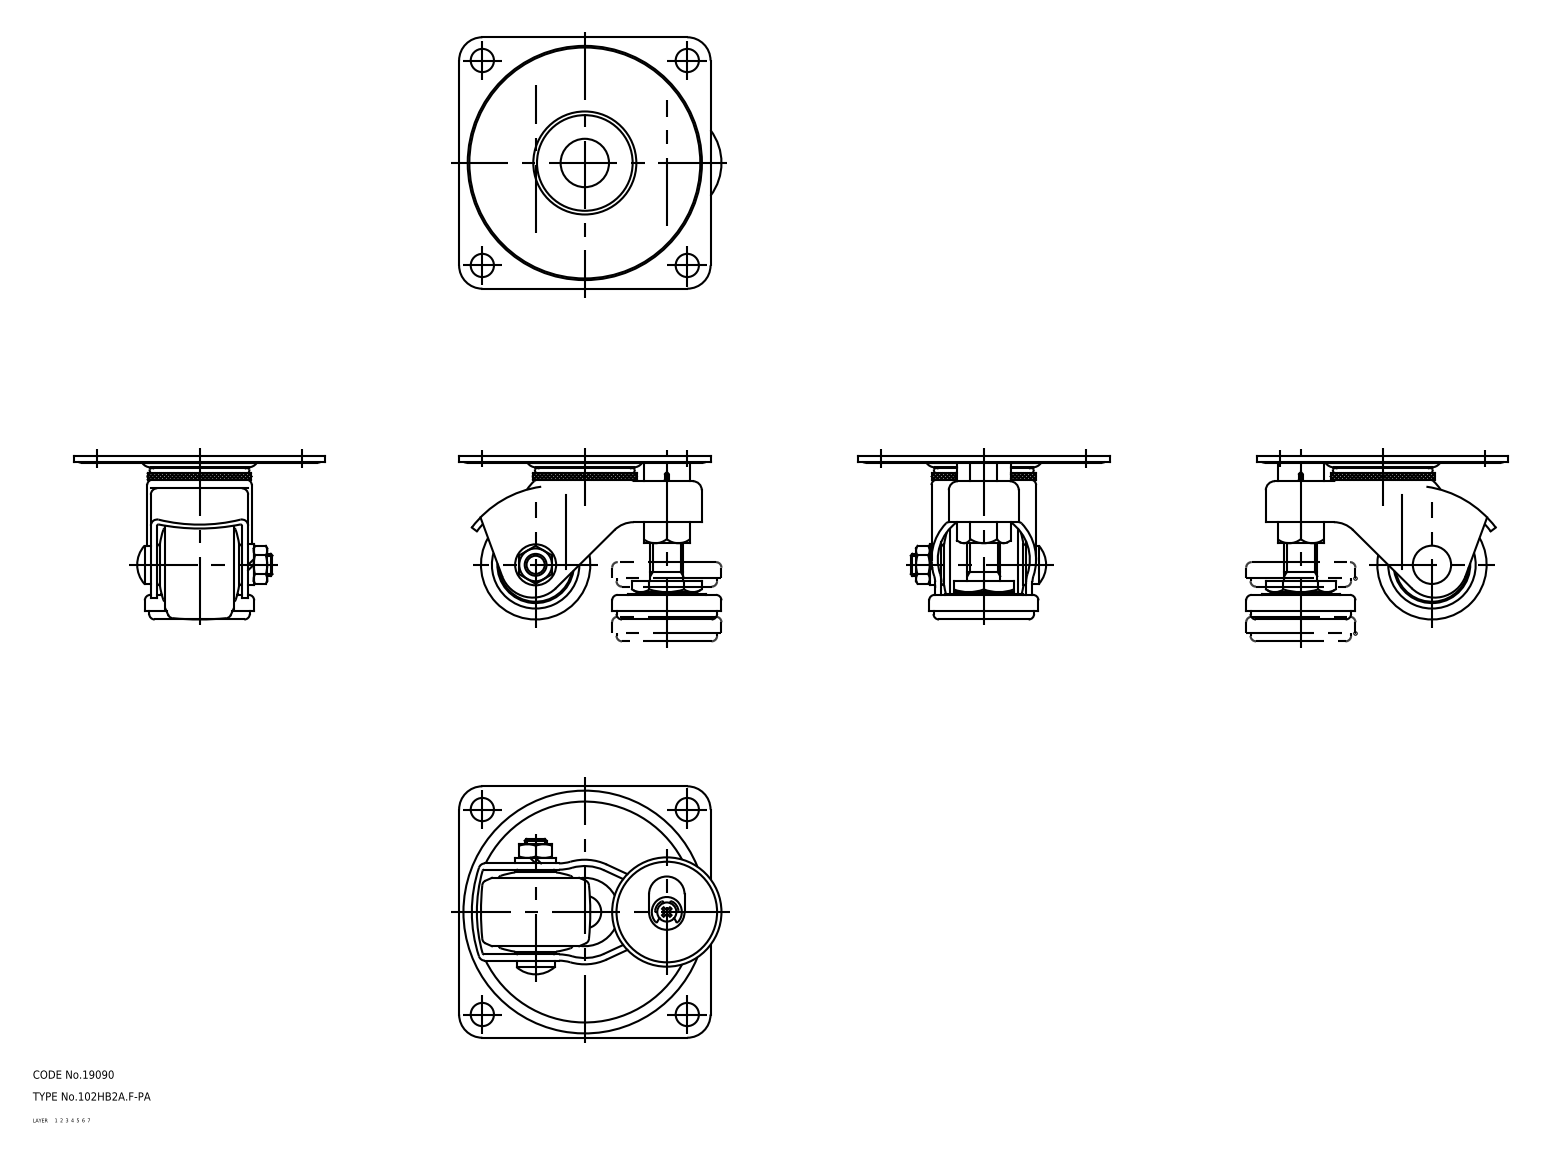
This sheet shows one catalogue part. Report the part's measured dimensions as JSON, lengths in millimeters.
{"part_name": "wheel; mounting plate; main shaft; foot (+2 more)", "step_written_by": "CADfix (AUTOMOTIVE_DESIGN)", "units": "millimeters", "bodies": {"solids": 6, "faces": 361, "planar": 0, "cylindrical": 0, "other": 361}, "overall_size": [96, 92, 60], "volume_mm3": 97455, "surface_area_mm2": 48648}
